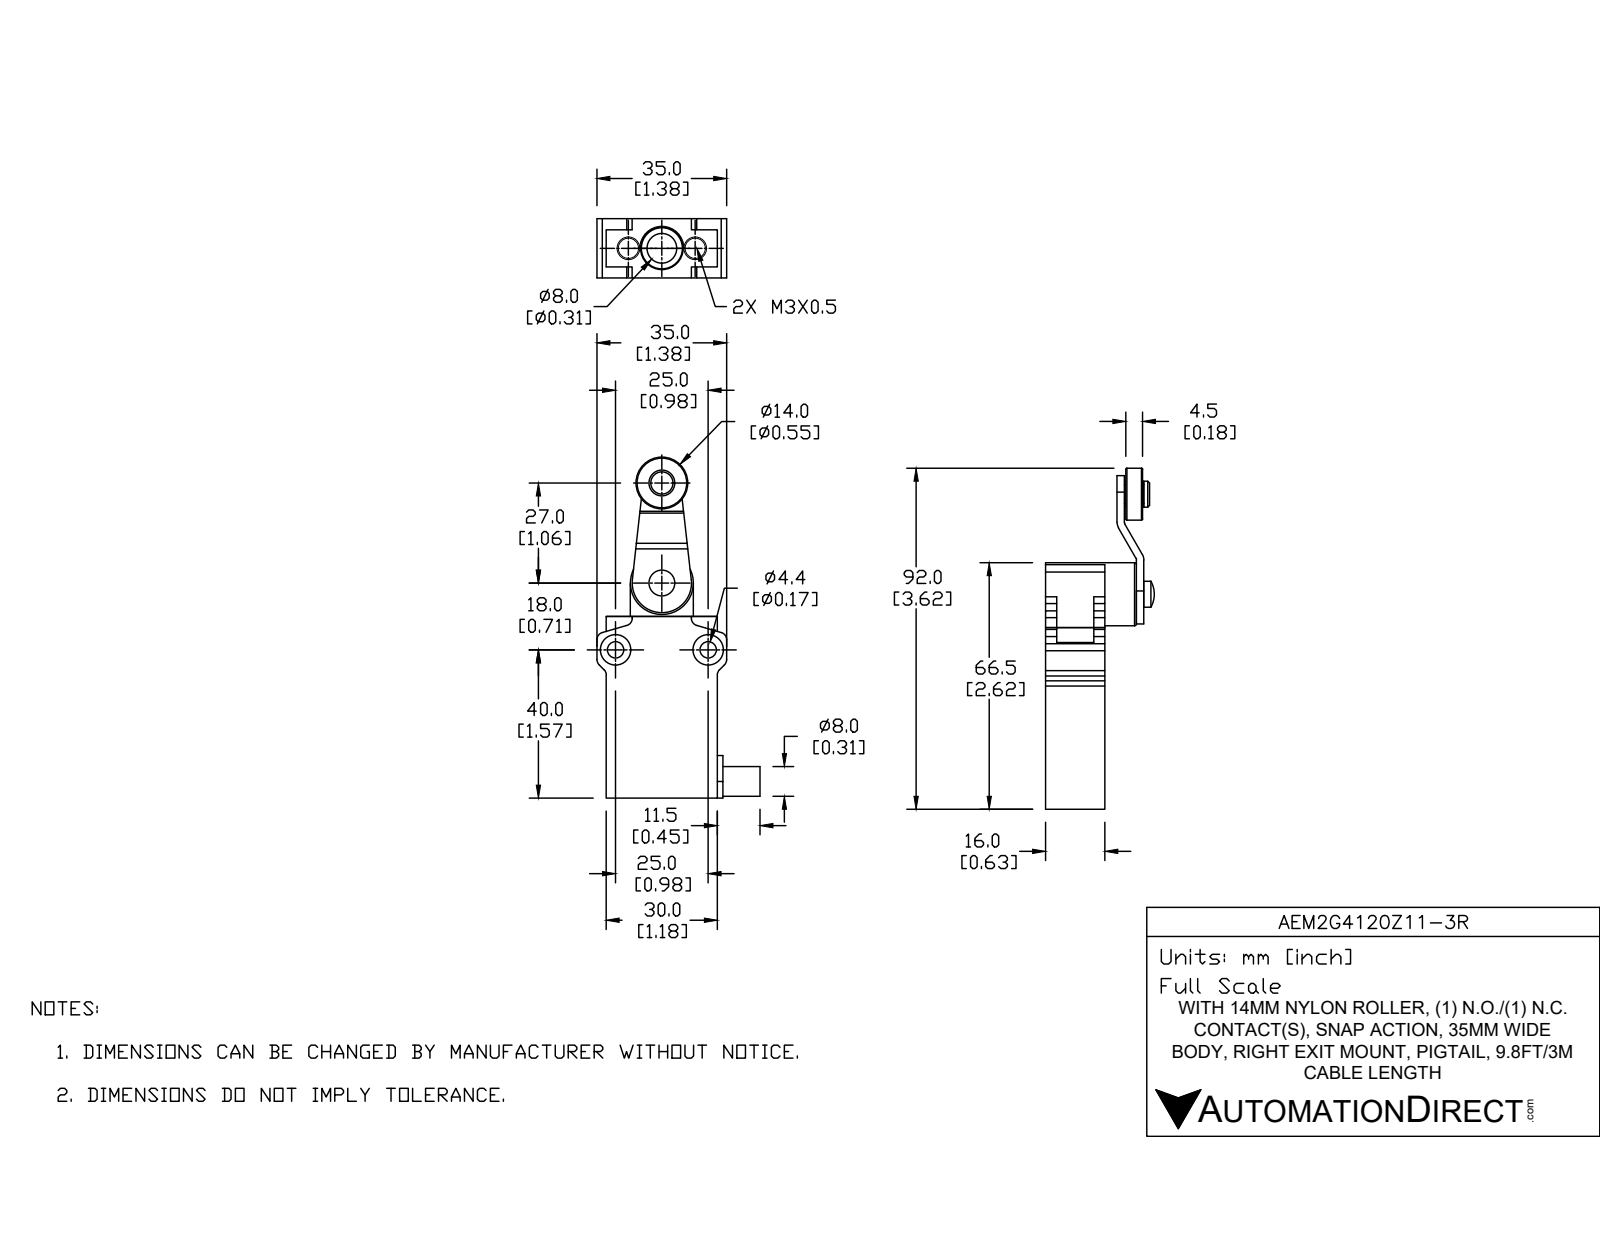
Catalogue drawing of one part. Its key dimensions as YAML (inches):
part_name: "AEM2G4120Z11-3R"
step_written_by: "SolidWorks 2017 (AUTOMOTIVE_DESIGN)"
units: inches
bodies: {solids: 7, faces: 543, planar: 297, cylindrical: 73, other: 173}
overall_size: [3.602, 1.87, 1.26]
volume: 1.855
surface_area: 17.74
round_holes:
  - {diameter: 0.118, count: 2}
  - {diameter: 0.173, count: 2}
  - {diameter: 0.323, count: 2}
  - {diameter: 0.098, count: 1}
  - {diameter: 0.138, count: 1}
  - {diameter: 0.161, count: 1}
  - {diameter: 0.197, count: 1}
  - {diameter: 0.224, count: 1}
round_bosses_or_shafts:
  - {diameter: 0.276, count: 2}
  - {diameter: 0.622, count: 1}
  - {diameter: 0.551, count: 1}
  - {diameter: 0.394, count: 1}
  - {diameter: 0.323, count: 1}
  - {diameter: 0.236, count: 1}
  - {diameter: 0.197, count: 1}
  - {diameter: 0.157, count: 1}
partial_cylinders:
  - {radius: 0.079, count: 8}
  - {radius: 0.039, count: 2}
  - {radius: 0.118, count: 2}
  - {radius: 0.256, count: 1}
  - {radius: 0.315, count: 1}
face_to_face_distances: [0.63, 1.181, 1.929, 0.354, 0.079, 0.984, 0.28, 0.902, 0.102, 0.472]
hole_center_spacings: [0.863, 1.82, 0.748, 0.984, 1.043]
